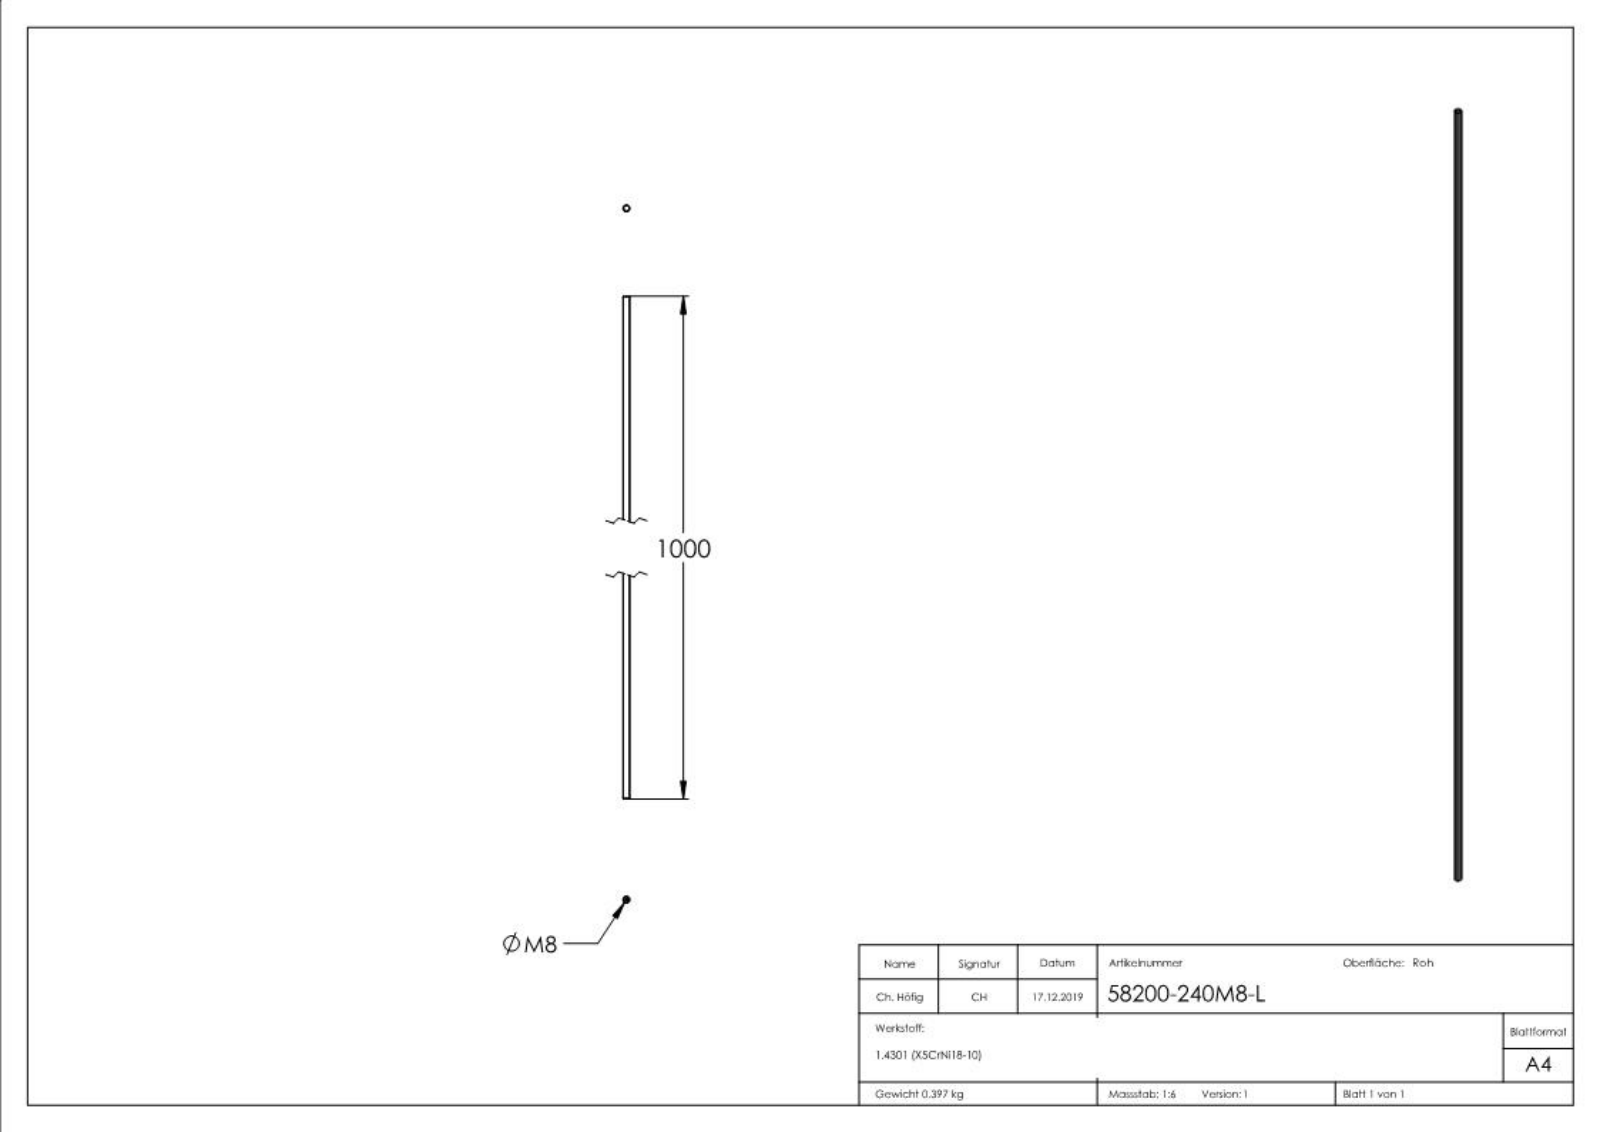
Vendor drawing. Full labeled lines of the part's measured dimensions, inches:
Part name (STEP PRODUCT): 58200-240M8-L
STEP written by: SolidWorks 2015 (CONFIG_CONTROL_DESIGN)
Units: inches
Bodies: 1 solid, 278 faces (146 planar, 1 cylindrical, 131 other)
Overall size (bounding box): 39.37 × 0.315 × 0.315
Volume: 3.066 in³ · Surface area: 39.06 in²
Round bosses / shafts (diameter × count): ⌀0.315 ×1
Main face-to-face distances: 39.37, 39.366, 0.014, 0.014, 0.044, 0.044, 0.058, 0.064, 0.013, 0.02
